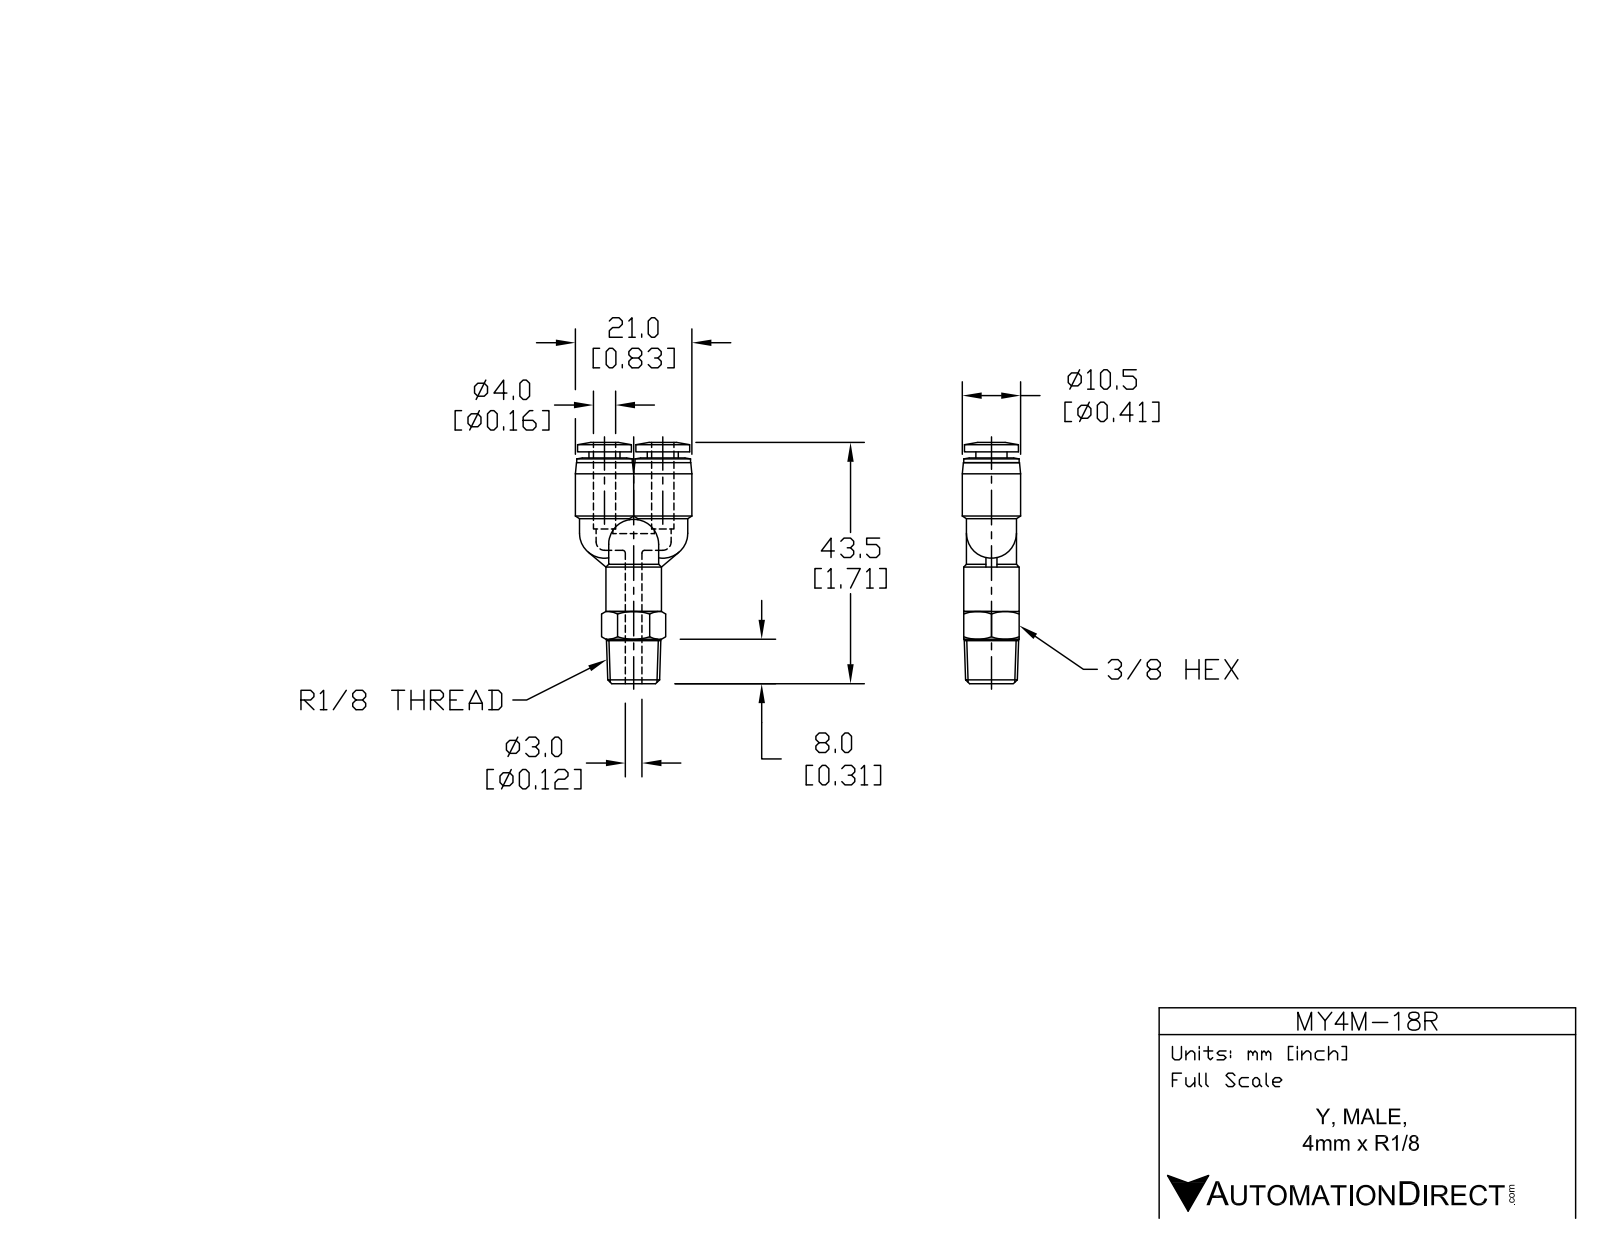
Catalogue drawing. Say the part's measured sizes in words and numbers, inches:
The part is named "MY4M-18R". Its 3-D file was written by "SolidWorks 2015 (AUTOMOTIVE_DESIGN)". It is 1 solid with 108 faces: 23 planar, 37 cylindrical and 48 other. Overall it measures 1.707 by 0.827 by 0.413 inches. Its volume is 0.248 cubic inches and its surface area 4.798 square inches. Round holes: 4 of diameter 0.118, 2 of diameter 0.169. Round bosses or shafts: 3 of diameter 0.394, 3 of diameter 0.354, 2 of diameter 0.413, 2 of diameter 0.382, 2 of diameter 0.22. The main face-to-face distances are 0.394, 0.043, 1.596, 1.64, 0.157, 0.236, 1.096, 0.5, 0.543, 0.079. The hole center spacings are 0.207, 0.413.
